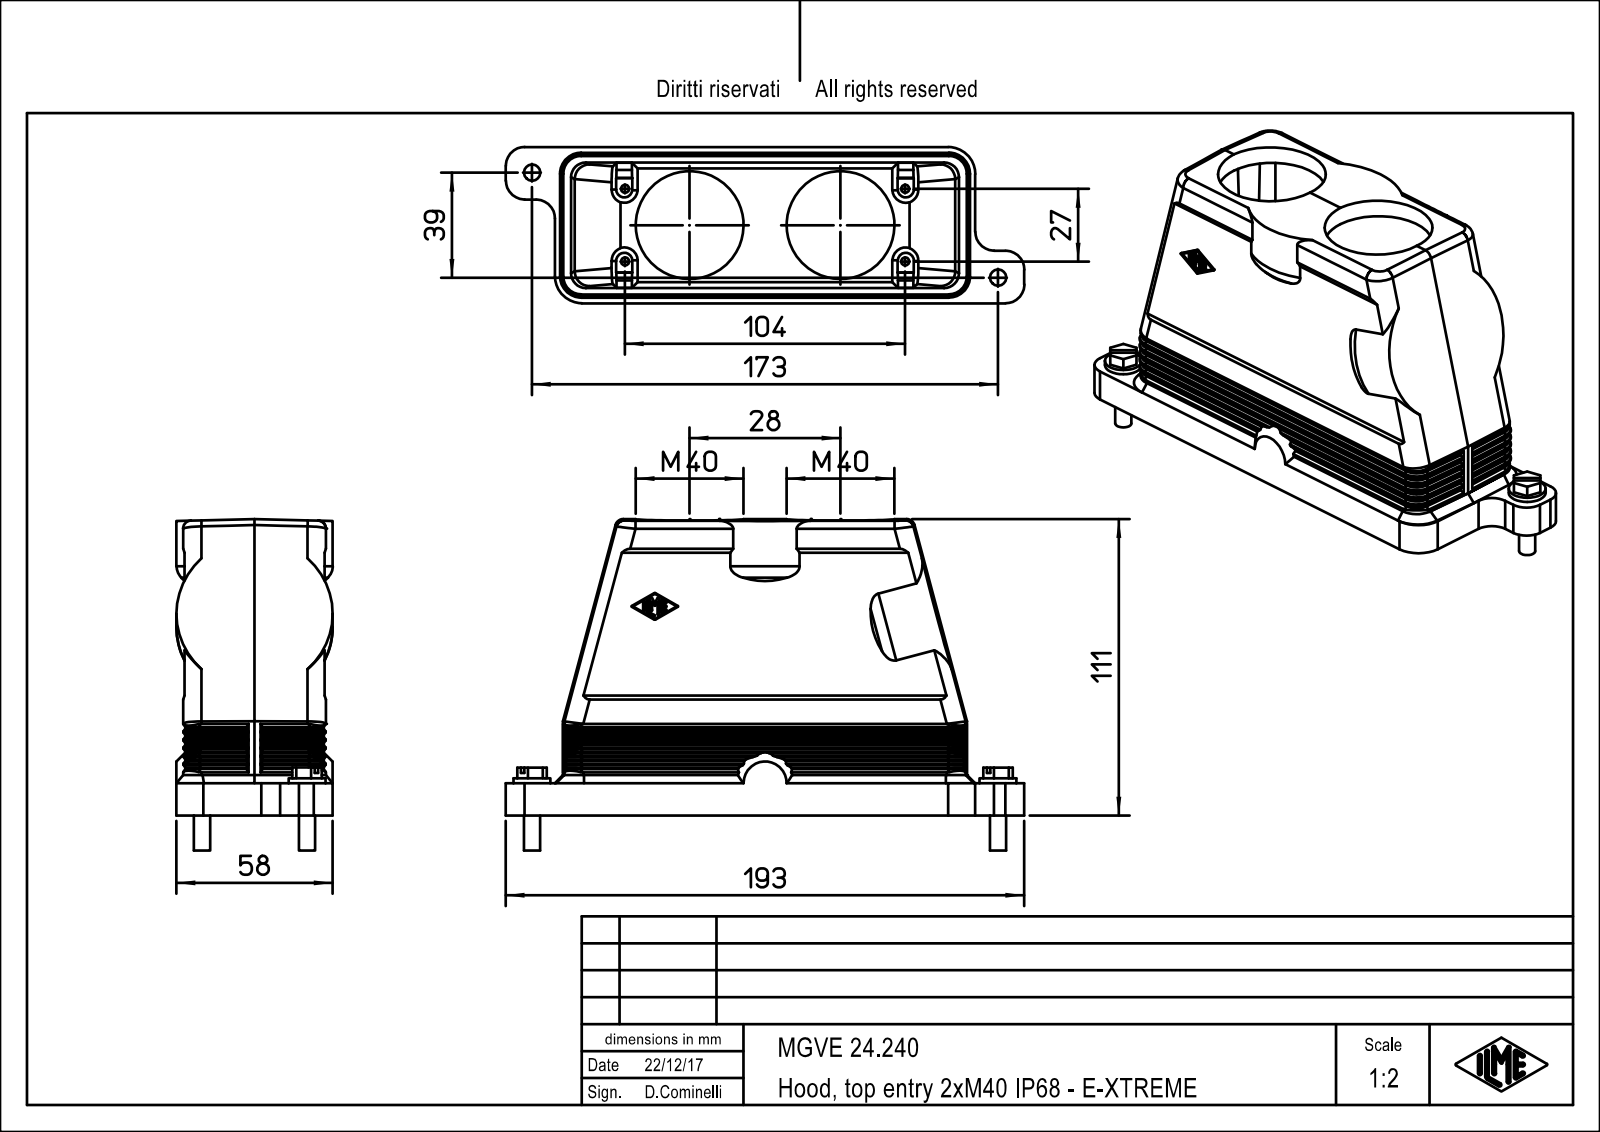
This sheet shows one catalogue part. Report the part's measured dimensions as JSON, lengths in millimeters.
{"part_name": "MGVE_24.240", "step_written_by": "PTC Creo Elements/Direct Modeling 19.0E 27-Jun-2016 (C) Parametric Technology GmbH (AUTOMOTIVE_DESIGN)", "units": "millimeters", "bodies": {"solids": 1, "faces": 535, "planar": 254, "cylindrical": 125, "other": 156}, "overall_size": [192.5, 123, 58], "volume_mm3": 205686, "surface_area_mm2": 96968, "round_holes": [[3, 4], [40, 2]], "round_bosses_or_shafts": [[13.7, 2], [6, 2]], "partial_cylinders_radius": [[7, 62], [0.33, 15], [5.5, 8], [7.3, 4], [0.17, 2], [10, 2], [29, 2], [0.17, 1]], "face_to_face_distances": [52, 3, 55, 0.5, 2.5, 55.5, 52.5, 3.33, 104.5, 58], "hole_center_spacings": [27.54, 81.13, 27, 104, 107.45, 56]}
